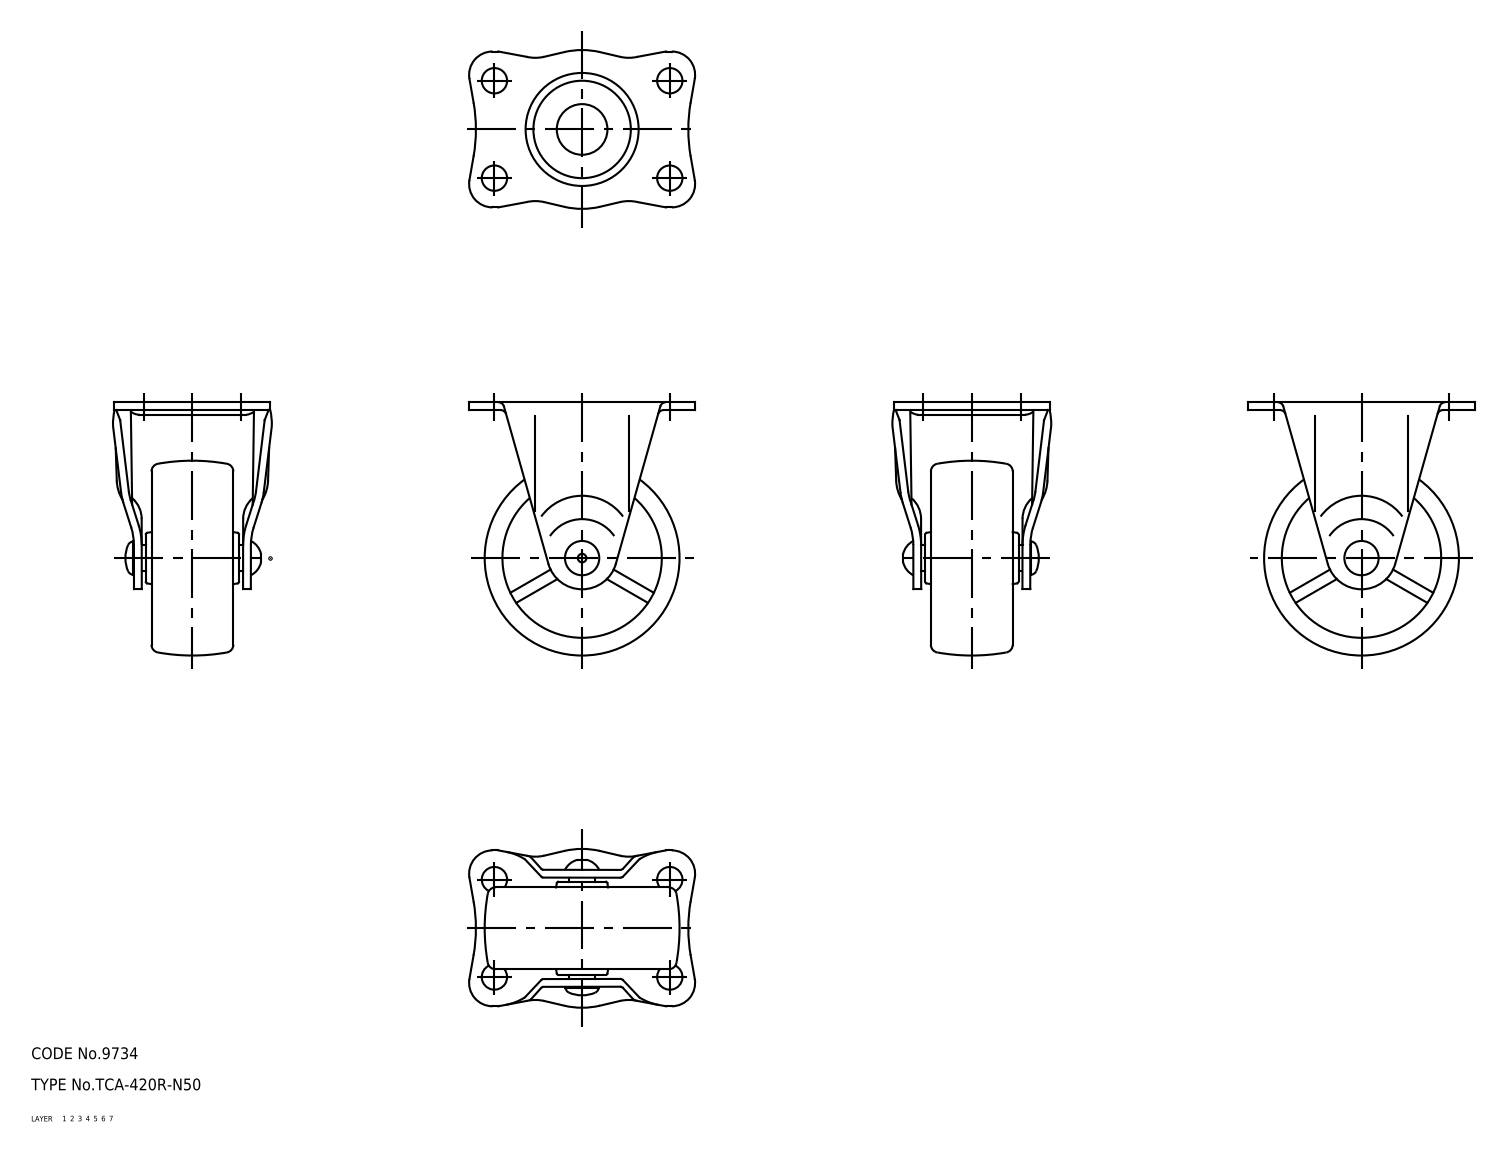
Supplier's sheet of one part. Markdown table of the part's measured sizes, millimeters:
| quantity | value |
| --- | --- |
| part name | wheel; axle; No_420_R_N50_4_361_36 |
| STEP written by | CADfix (AUTOMOTIVE_DESIGN) |
| units | millimeters |
| bodies | 3 solids, 287 faces (0 planar, 0 cylindrical, 287 other) |
| overall size | 65 × 58 × 40 |
| volume | 38 342 mm³ |
| surface area | 19 402 mm² |
